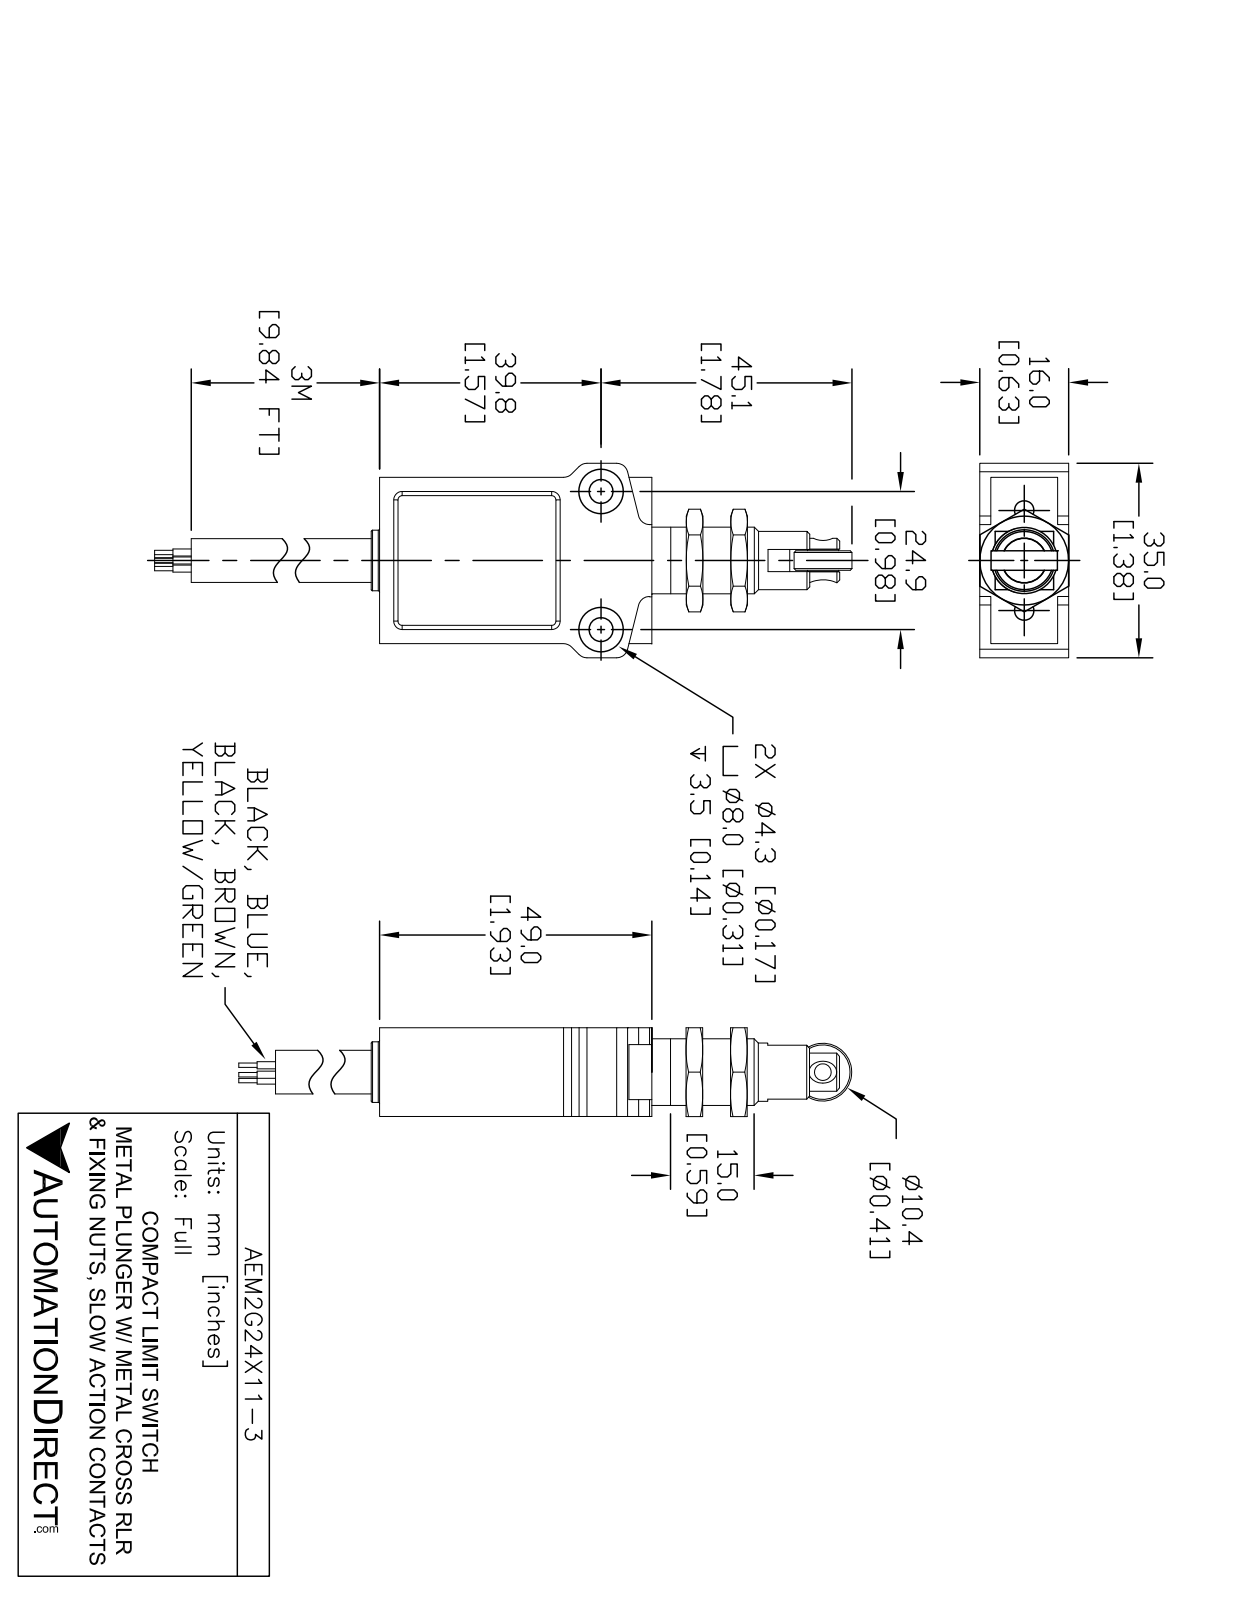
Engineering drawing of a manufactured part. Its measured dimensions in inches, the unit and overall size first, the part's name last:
Units: inches
Overall size (bounding box): 3.965 × 1.38 × 0.63
Round holes (diameter × count): ⌀0.177 ×2, ⌀0.344 ×2
Round bosses / shafts (diameter × count): ⌀0.05 ×5, ⌀0.031 ×5, ⌀0.41 ×2, ⌀0.47 ×1, ⌀0.43 ×1, ⌀0.31 ×1
Partial cylindrical surfaces — rounded edges, fillets, slot ends (radius × count): R0.03 ×8, R0.08 ×8, R0.135 ×1
Main face-to-face distances: 0.03, 0.6, 0.57, 0.63, 1.18, 0.12, 0.3, 1.93, 0.187, 0.443
Hole centre spacings: 0.98
Volume: 1.565 in³ · Surface area: 14.03 in²
Bodies: 2 solids, 191 faces (98 planar, 47 cylindrical, 46 other)
Part name (STEP PRODUCT): AEM2G24X11-3_Default
STEP written by: SolidWorks 2021 (CONFIG_CONTROL_DESIGN)
